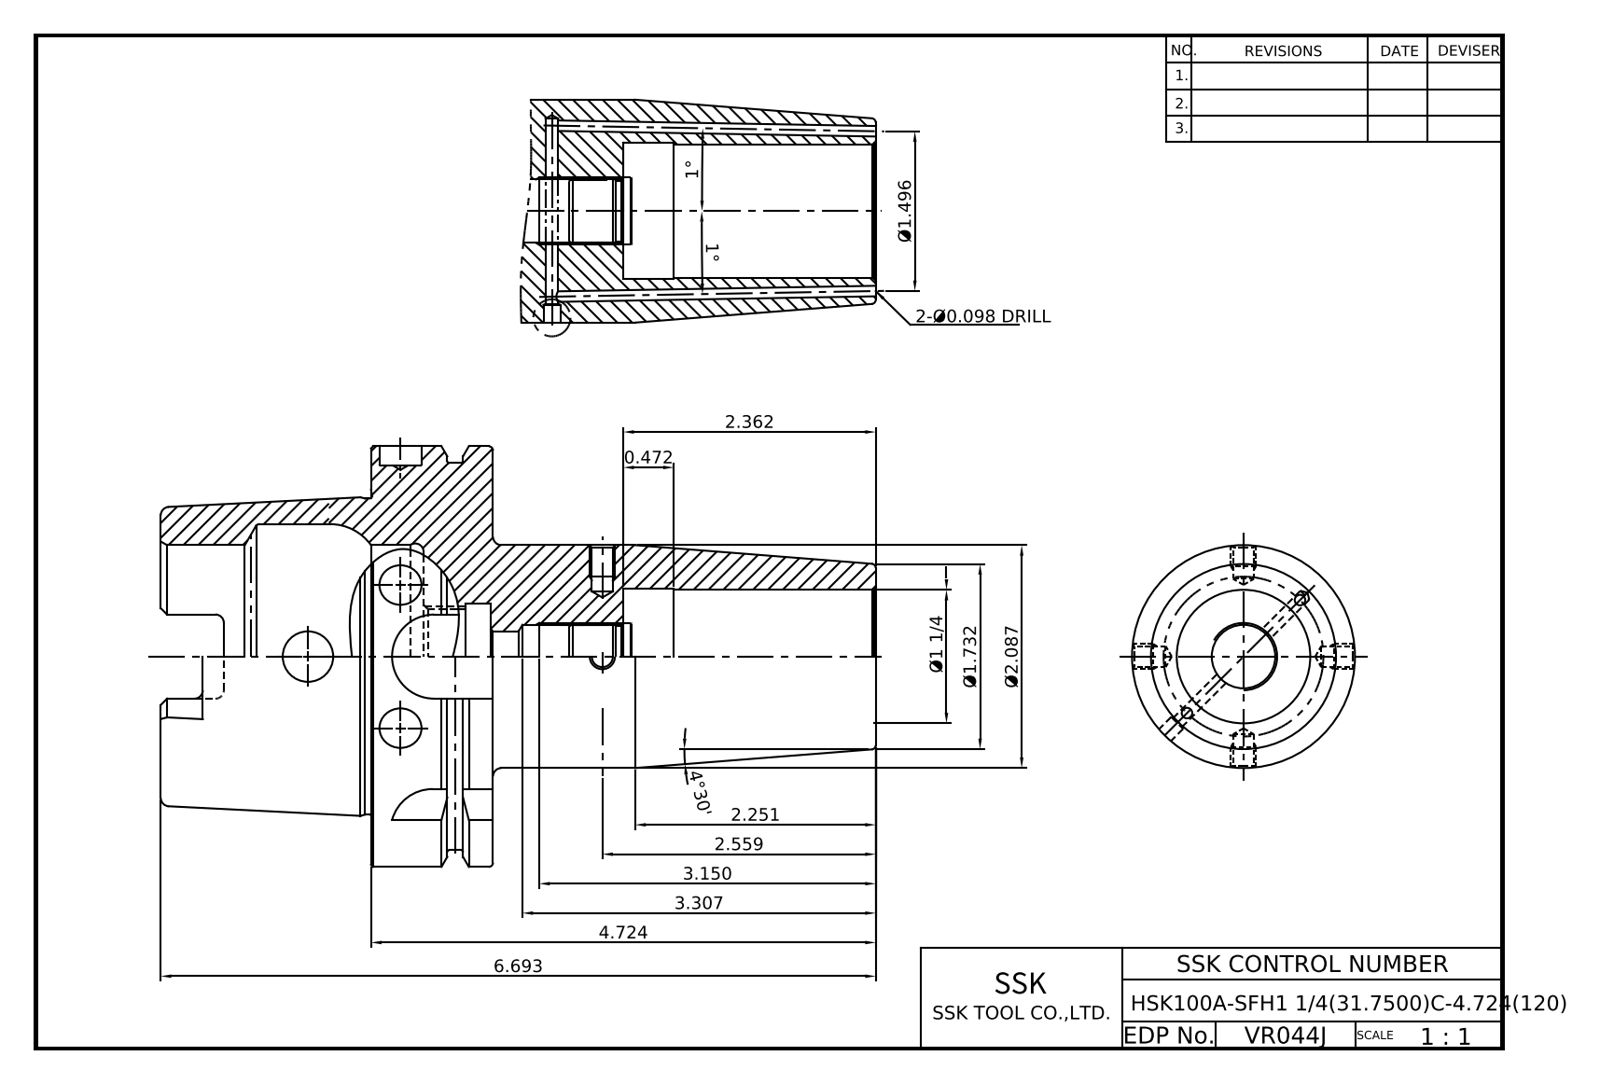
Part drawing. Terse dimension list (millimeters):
name: LO-HSK100A-SFH31.75C-120
written by: Autodesk Inventor 2022 (AUTOMOTIVE_DESIGN)
unit: mm
bodies: 1 solid, 119 faces (38 planar, 37 cylindrical, 44 other)
size: 170 × 100 × 100
volume: 380 792 mm³; area: 71 704 mm²
holes: 2× ⌀2.5, 2× ⌀12, 1× ⌀10, 1× ⌀14.92, 1× ⌀22.38, 1× ⌀25, 1× ⌀31.75, 1× ⌀32.95, 1× ⌀53, 1× ⌀63
bosses: 1× ⌀100, 1× ⌀92, 1× ⌀75.41
rounds: 6× R2, 4× R4.88, 4× R10
face distances: 29, 12.5, 16.5, 60, 62.5, 50, 79, 47.5, 110, 31
